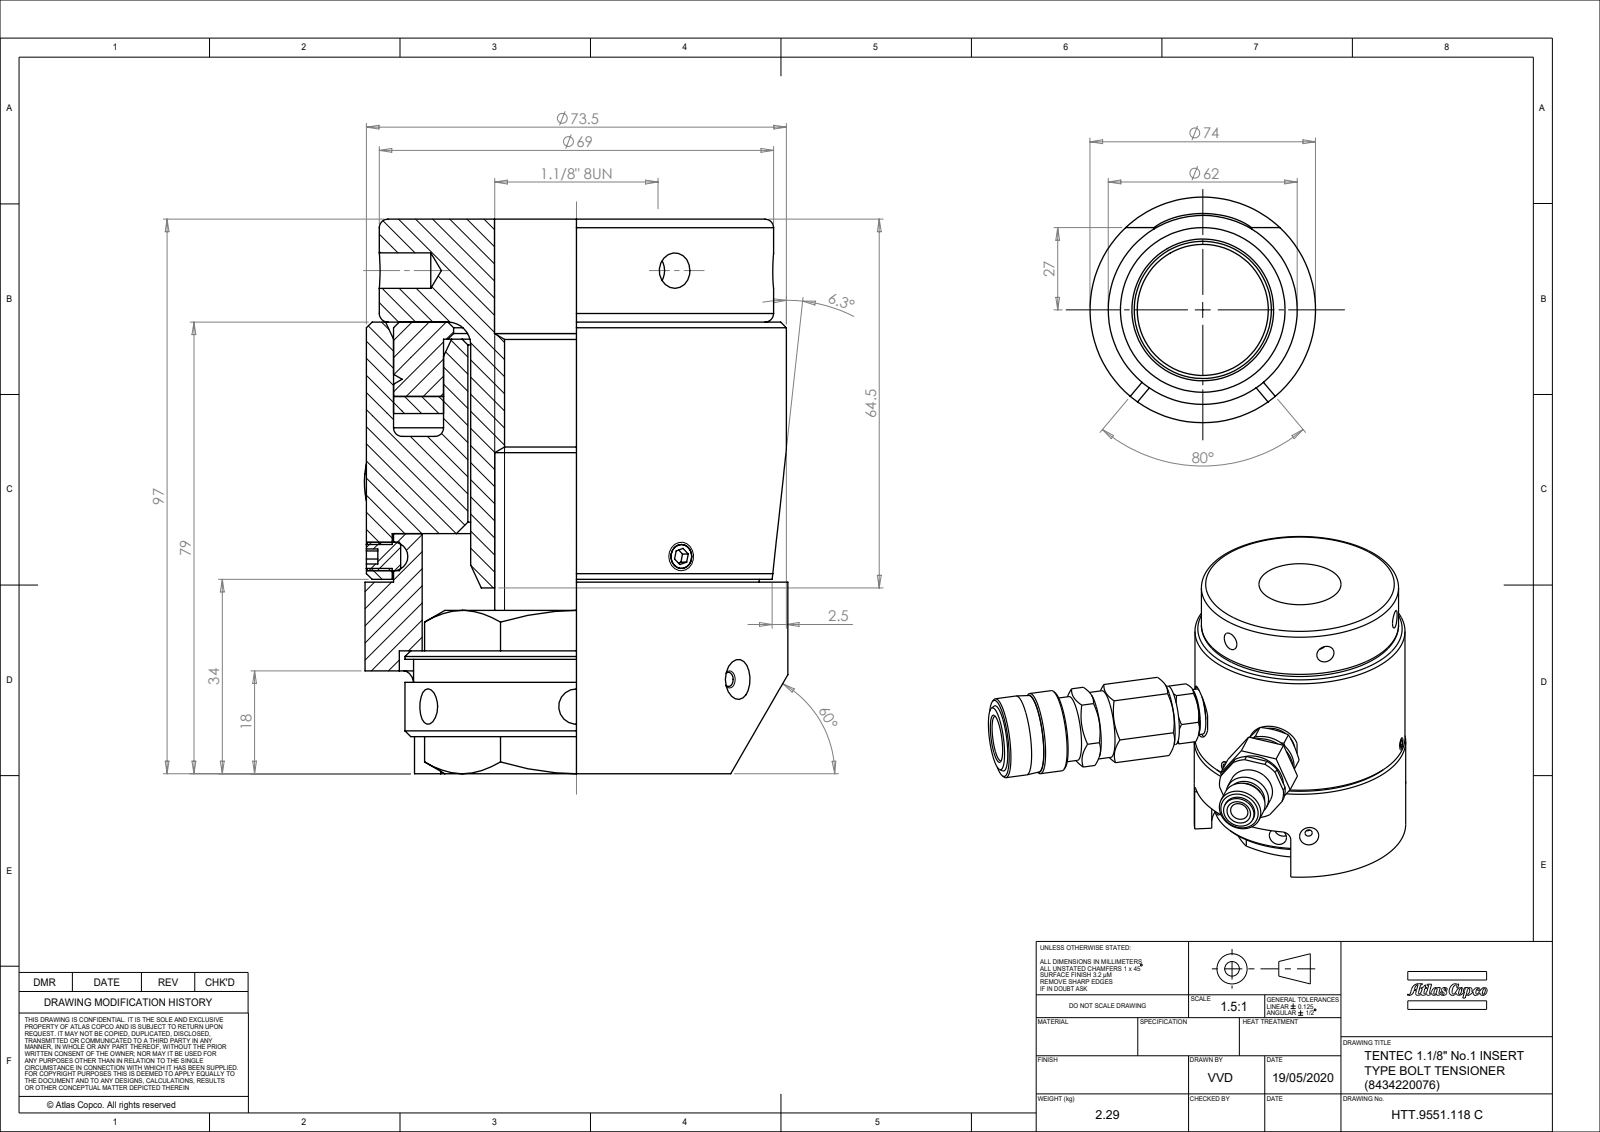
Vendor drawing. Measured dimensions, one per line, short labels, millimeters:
name: ASM0006_SW0001
written by: CREO PARAMETRIC BY PTC INC, 2020281 (CONFIG_CONTROL_DESIGN)
unit: mm
bodies: 1 solid, 413 faces (129 planar, 143 cylindrical, 141 other)
size: 138.1 × 113.3 × 97
volume: 401 200 mm³; area: 69 740 mm²
holes: 6× ⌀6.2, 4× ⌀2.5, 2× ⌀2, 2× ⌀8.7, 2× ⌀9, 2× ⌀11.6, 1× ⌀3, 1× ⌀15, 1× ⌀15.6, 1× ⌀28.7, 1× ⌀48, 1× ⌀62
bosses: 3× ⌀5, 2× ⌀20.6, 2× ⌀15.9, 2× ⌀12, 1× ⌀74, 1× ⌀73.5, 1× ⌀69, 1× ⌀64
rounds: 8× R9, 2× R3, 1× R11.6, 1× R20
face distances: 97, 18, 46.1, 79, 1, 46.5, 32.5, 64.5, 63.5, 24
hole spacings: 39.2, 27.8
